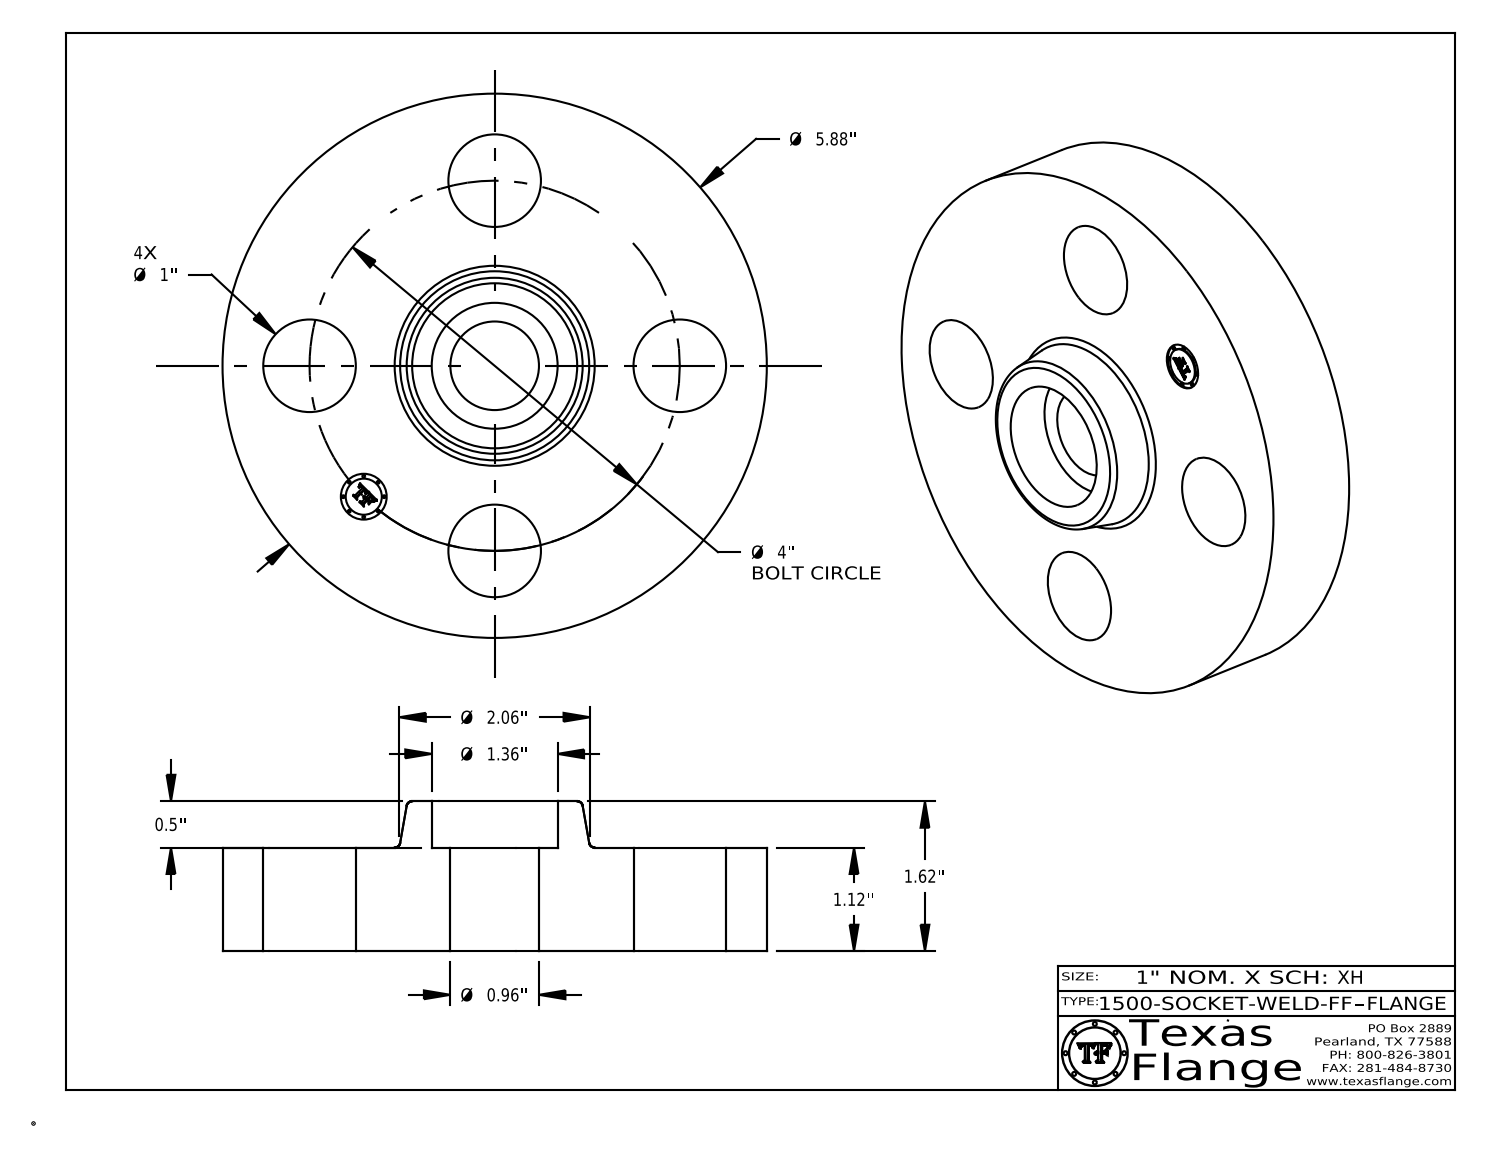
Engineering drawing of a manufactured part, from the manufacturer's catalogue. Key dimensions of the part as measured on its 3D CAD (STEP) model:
Part name (STEP PRODUCT): 1500-SOCKET-WELD-FF
STEP written by: CATIA V5 STEP AP214 (AUTOMOTIVE_DESIGN)
Units: inches
Bodies: 1 solid, 409 faces (369 planar, 34 cylindrical, 6 other)
Overall size (bounding box): 5.88 × 5.88 × 1.62
Volume: 26.89 in³ · Surface area: 89.34 in²
Round holes (diameter × count): ⌀1 ×4, ⌀0.495 ×1, ⌀0.957 ×1, ⌀1.36 ×1
Round bosses / shafts (diameter × count): ⌀0.03 ×8, ⌀5.88 ×1, ⌀0.39 ×1
Main face-to-face distances: 1.12, 1.62, 0.5, 0.015, 1.105, 0.515, 0.148, 0.145, 0.027, 0.096
Hole centre spacings: 2, 2.828, 1.531, 3.695, 4
